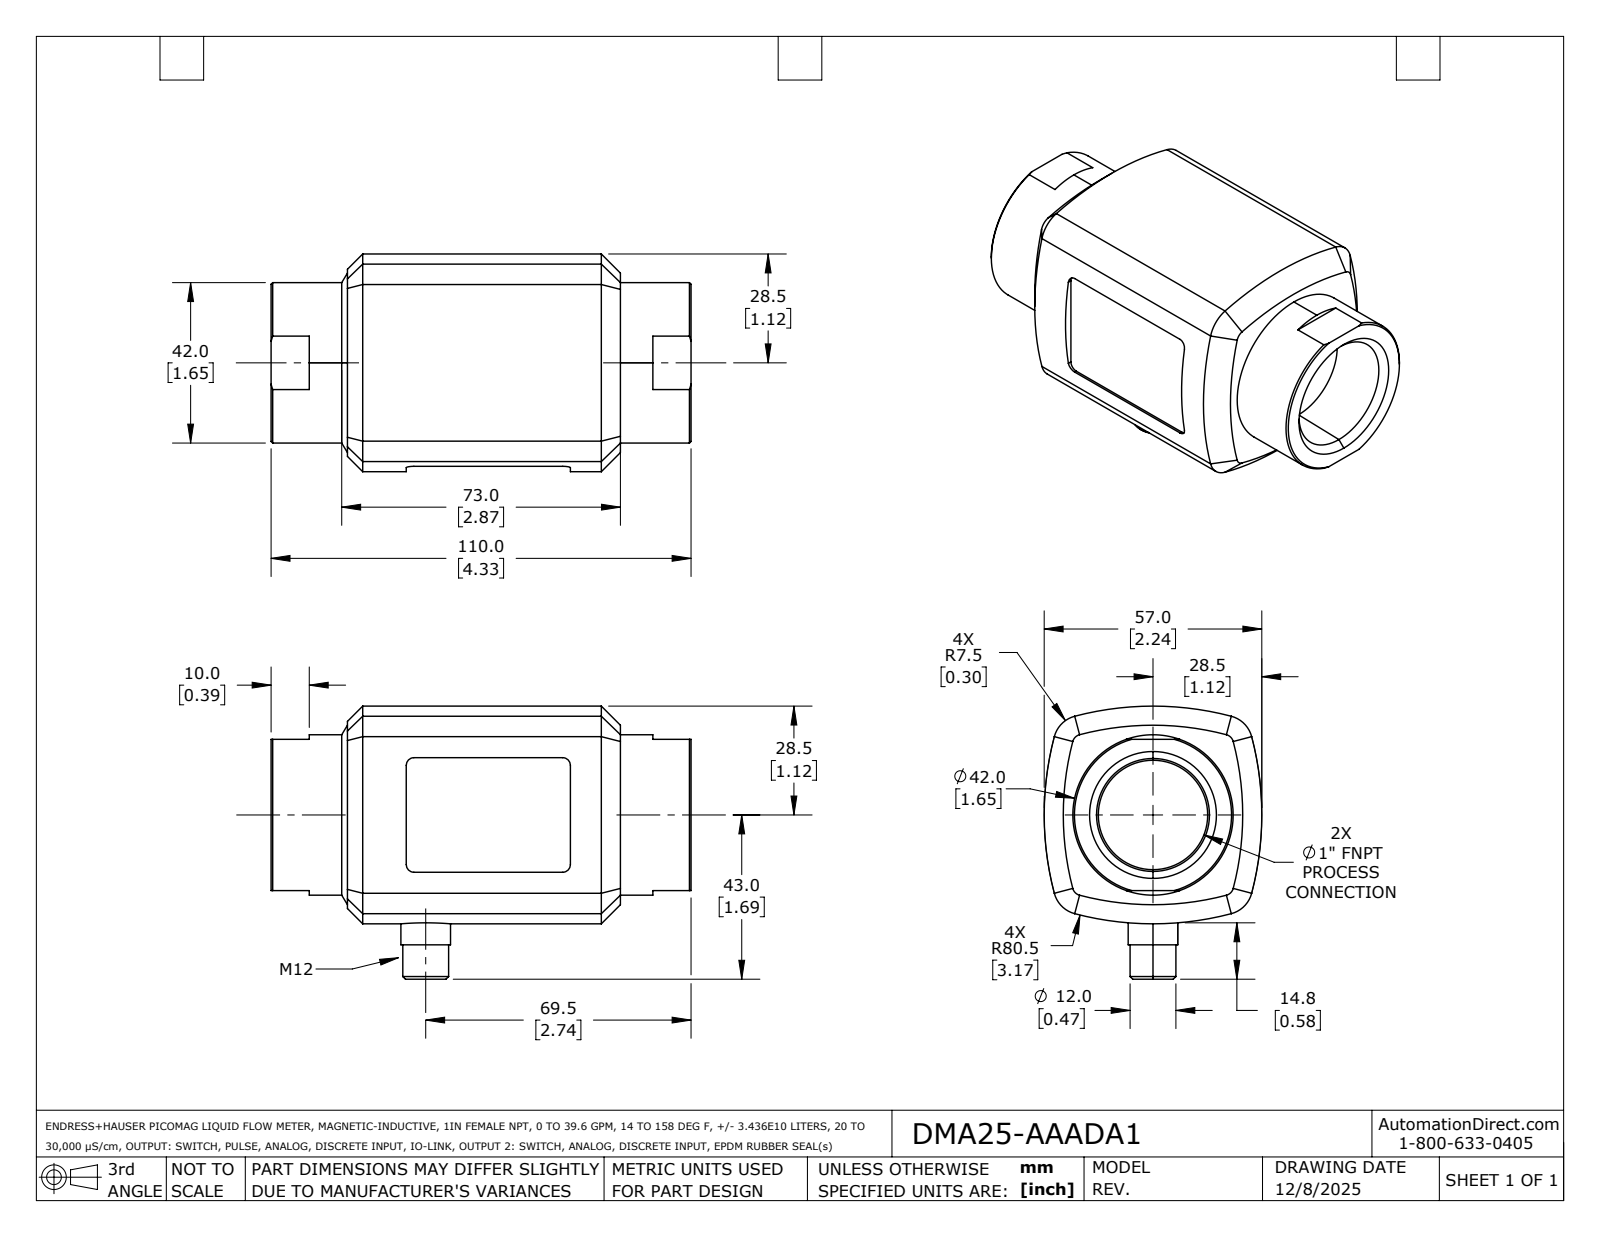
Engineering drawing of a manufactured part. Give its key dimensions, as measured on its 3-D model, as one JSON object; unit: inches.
{"part_name": "DMA25-AAADA1", "step_written_by": "SolidWorks 2024 (AUTOMOTIVE_DESIGN)", "units": "inches", "bodies": {"solids": 1, "faces": 76, "planar": 22, "cylindrical": 22, "other": 32}, "overall_size": [4.331, 2.815, 2.244], "volume_in3": 14.34, "surface_area_in2": 42.62, "round_holes": [[0.382, 1]], "round_bosses_or_shafts": [[1.654, 1], [0.512, 1], [0.472, 1]], "partial_cylinders_radius": [[0.079, 4], [0.295, 4], [3.169, 4]], "face_to_face_distances": [0.661, 3.67, 3.009, 2.941, 0.067, 0.787, 3.543, 0.126, 2.815, 2.882]}
